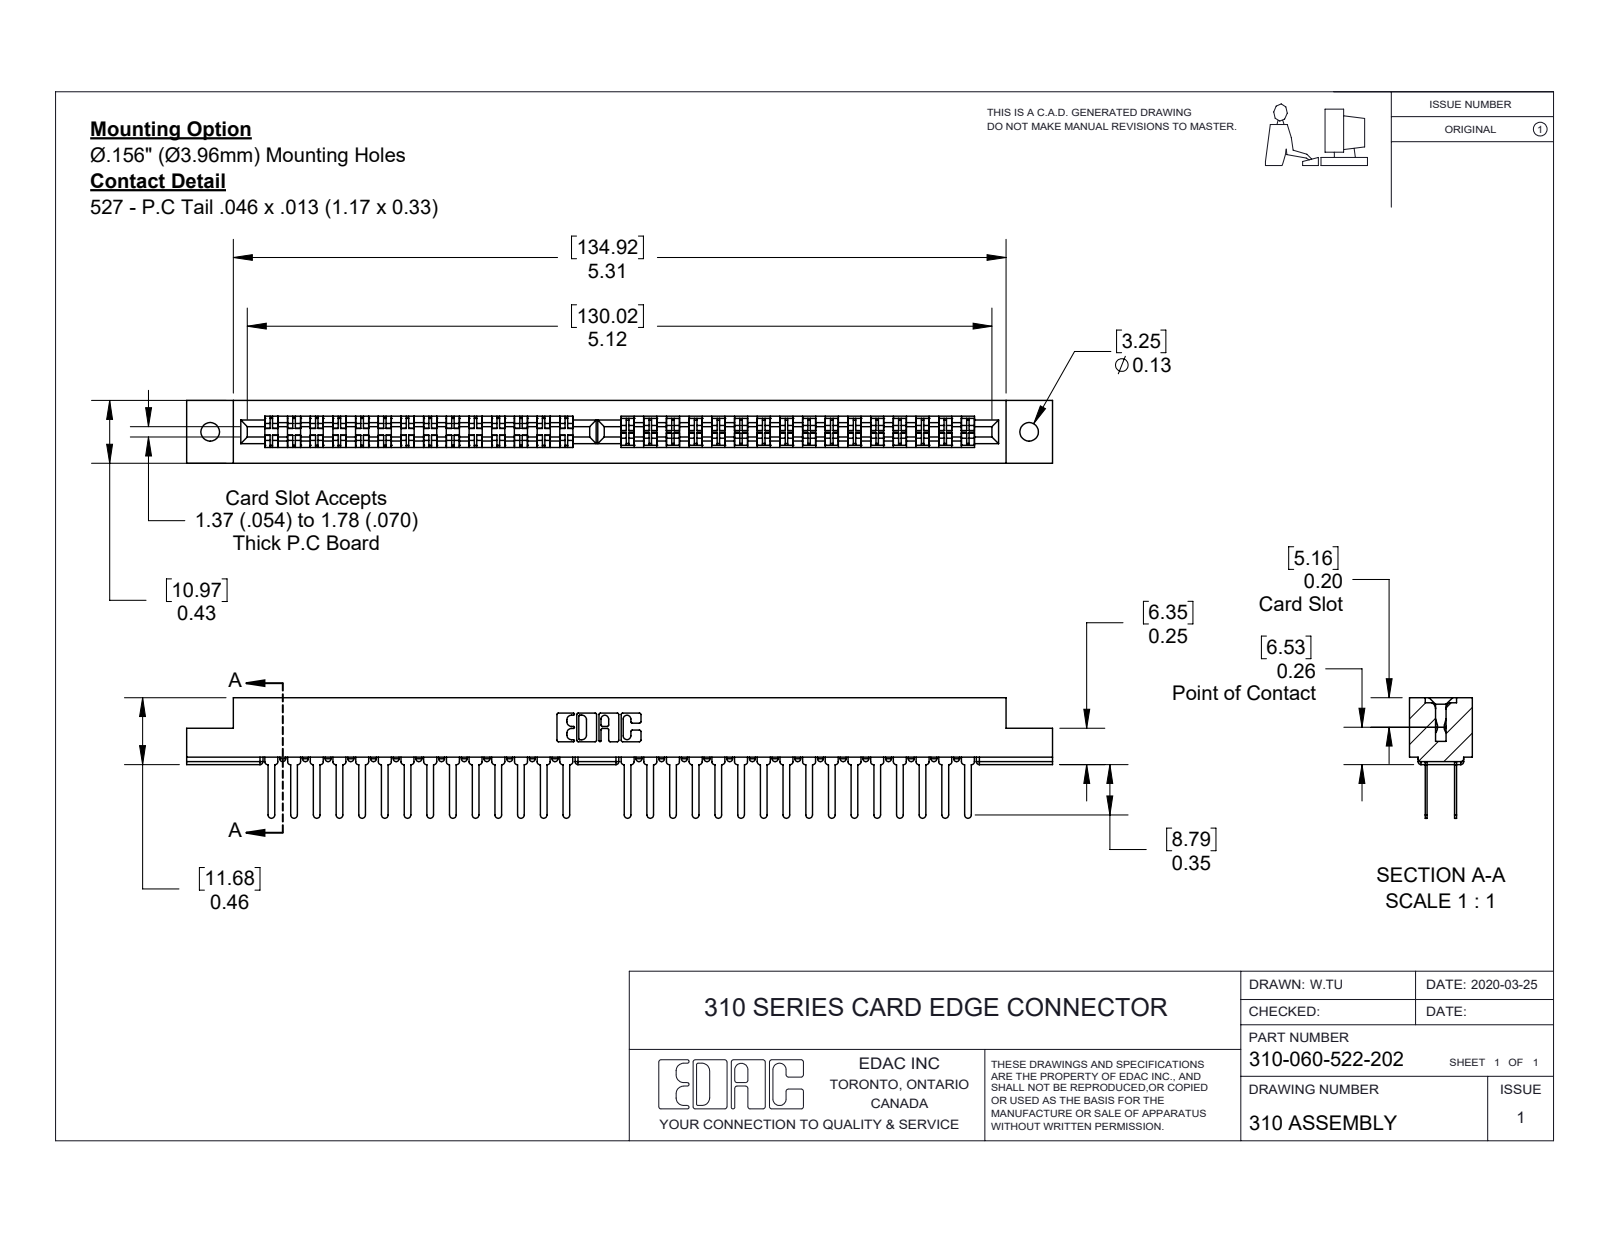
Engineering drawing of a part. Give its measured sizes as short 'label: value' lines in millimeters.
name: 310 Part_.128 Dia. Hole; 310-060-522-202; 307-290-001_522
written by: SolidWorks 2016 (CONFIG_CONTROL_DESIGN)
unit: mm
bodies: 61 solids, 2926 faces (1944 planar, 918 cylindrical, 64 other)
size: 151.21 × 21.06 × 10.97
volume: 13 103 mm³; area: 18 274 mm²
holes: 2× ⌀3.25
rounds: 158× R0.51, 30× R0.58, 22× R0.25, 6× R0.17, 6× R0.8, 4× R0.3, 4× R0.64, 4× R1.19
face distances: 2.76, 8.22, 0.33, 0.38, 4.75, 10.98, 3.14, 7.84, 5.08, 5.46
hole spacings: 143
